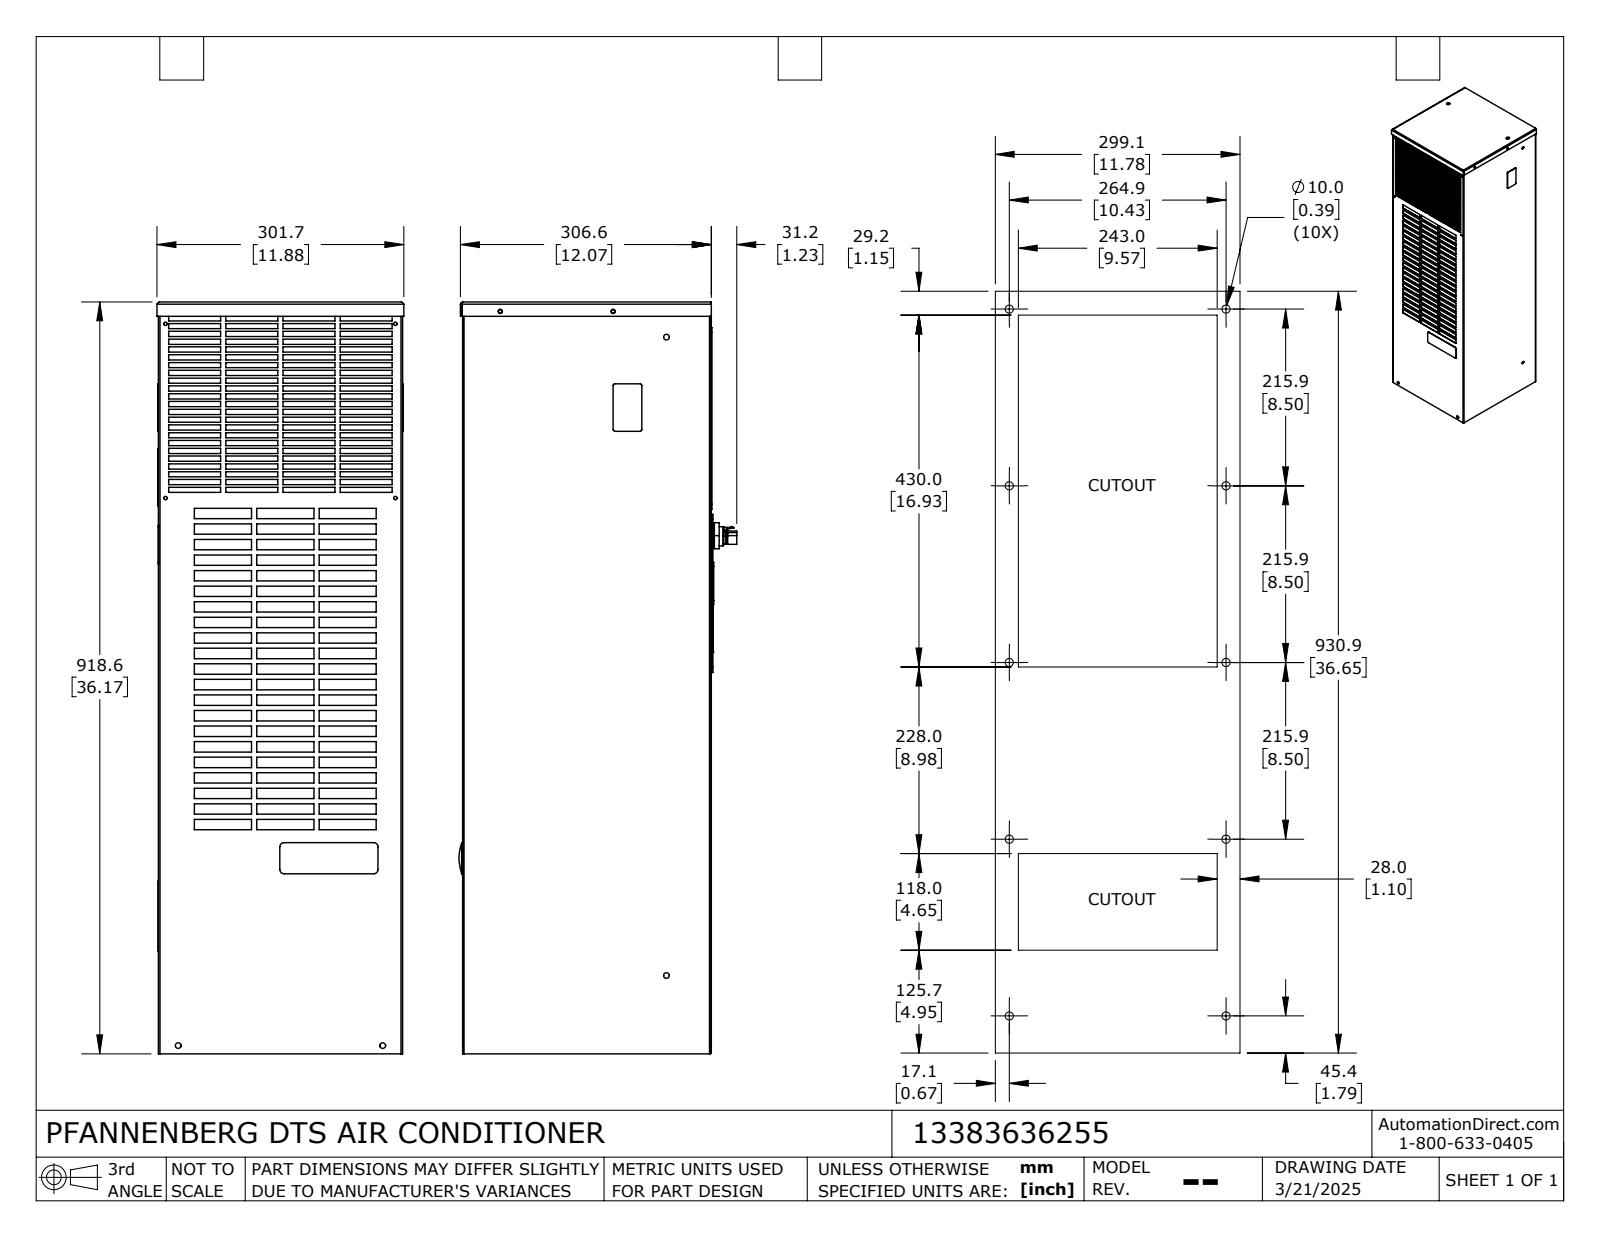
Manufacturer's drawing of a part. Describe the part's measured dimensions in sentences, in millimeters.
The part is named "13383636255_Default". Its 3-D file was written by "SolidWorks 2024 (CONFIG_CONTROL_DESIGN)". It is 1 solid with 1716 faces: 1188 planar, 475 cylindrical and 53 other. Overall it measures 918.6 by 339.7 by 301.7 millimeters. Its volume is 81 100 000 cubic millimeters and its surface area 2 398 000 square millimeters. Round holes: 29 of diameter 4.2, 10 of diameter 4.8, 6 of diameter 7, 5 of diameter 4.3, 5 of diameter 5.3, 4 of diameter 3.1, 4 of diameter 4.1, 2 of diameter 4.3, 2 of diameter 5.2, 2 of diameter 10, 2 of diameter 24, 1 of diameter 8. Round bosses or shafts: 4 of diameter 2, 2 of diameter 22, 1 of diameter 35, 1 of diameter 23. Partial cylindrical surfaces (rounded edges, fillets, slot ends): 112 of radius 3.2, 13 of radius 0.8, 12 of radius 2, 12 of radius 5, 10 of radius 2.2, 10 of radius 6, 4 of radius 2, 4 of radius 3.2. The main face-to-face distances are 300, 298.5, 1.1, 1.4, 300.8, 0.8, 2.1, 302.1, 302.9, 1.9. The hole center spacings are 7.5, 6.2, 38, 5.9, 6.5, 11.5, 16.6, 16.6.
